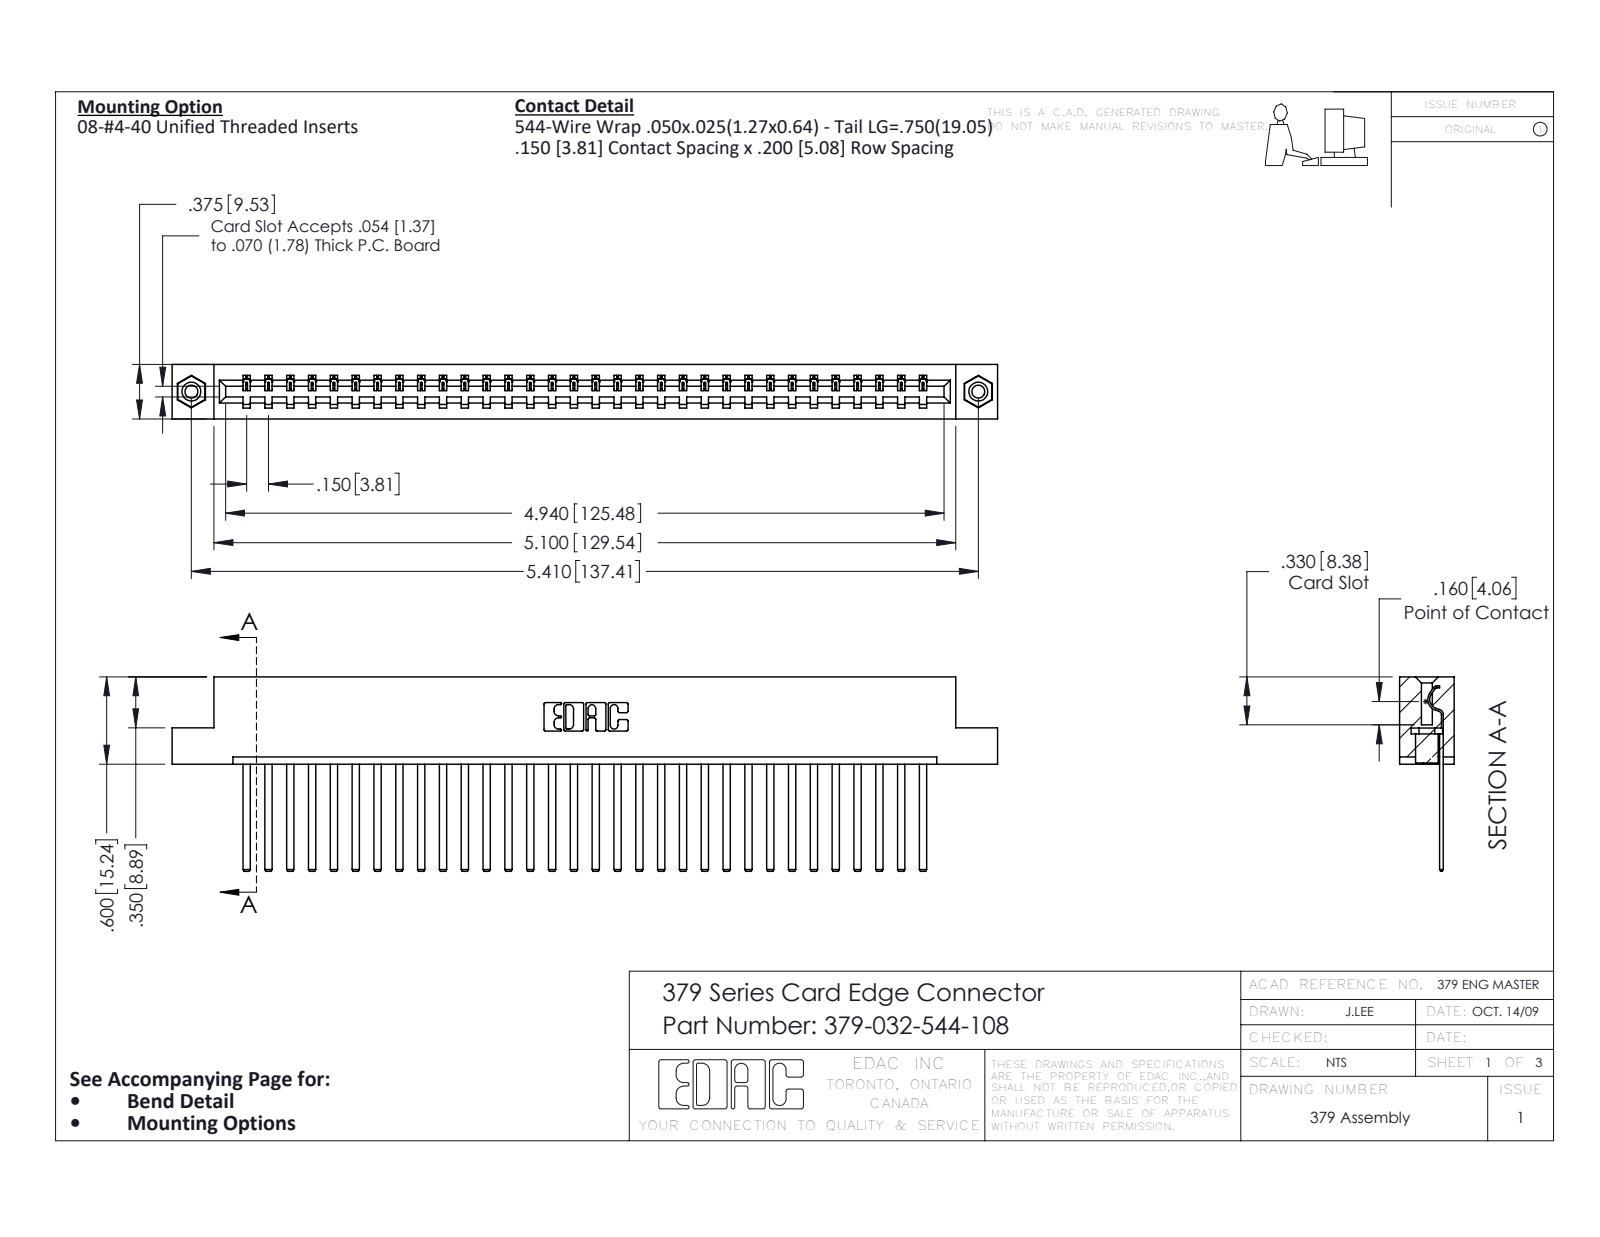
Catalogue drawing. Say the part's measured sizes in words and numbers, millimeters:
The part is named "379-032-544-108; 345-250-001_345-250-003-102; 345-292-001_345-293-144; 379 Part_Flush - .156 Dia - TI". Its 3-D file was written by "SolidWorks 2016 (CONFIG_CONTROL_DESIGN)". It is 35 solids with 1838 faces: 1318 planar, 504 cylindrical and 16 other. Overall it measures 144.1 by 34 by 9.5 millimeters. Its volume is 15 400 cubic millimeters and its surface area 16 950 square millimeters. Round holes: 2 of diameter 2.3, 2 of diameter 3.2, 2 of diameter 4. Round bosses or shafts: 2 of diameter 3.9. Partial cylindrical surfaces (rounded edges, fillets, slot ends): 64 of radius 0.2, 22 of radius 0.3, 6 of radius 0.2, 6 of radius 0.8, 3 of radius 0.7, 1 of radius 0.4, 1 of radius 0.6, 1 of radius 0.6. The main face-to-face distances are 7.6, 1.9, 9.5, 7, 2.5, 0.6, 5.7, 15.2, 5.1, 3.8. The hole center spacings are 137.4.
